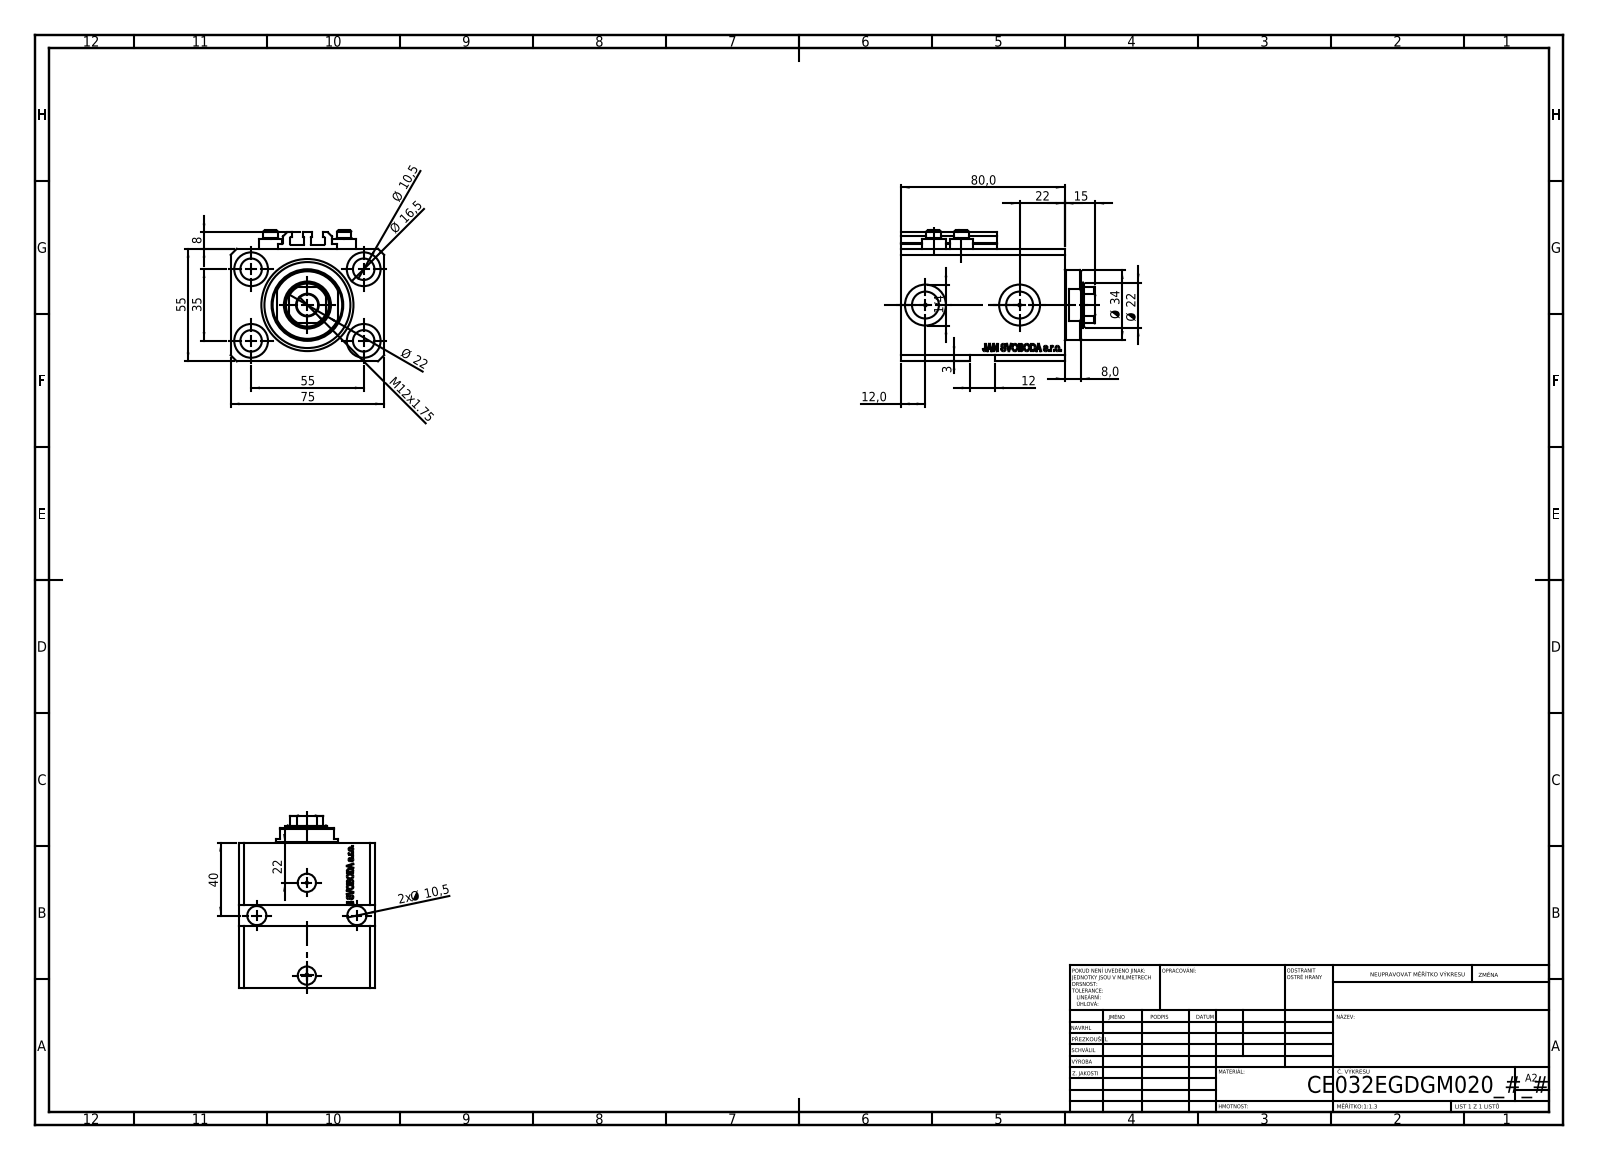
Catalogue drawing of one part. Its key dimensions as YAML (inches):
part_name: "ALLEN BOLT V250CE; V250CE_C_VCP; V250CE_VC_E; V250CE_E_Body"
step_written_by: "SolidWorks 2019 (CONFIG_CONTROL_DESIGN)"
units: inches
bodies: {solids: 8, faces: 1080, planar: 518, cylindrical: 138, other: 424}
overall_size: [3.74, 2.953, 2.52]
volume: 17.1
surface_area: 117.2
round_holes:
  - {diameter: 0.413, count: 7}
  - {diameter: 0.049, count: 4}
  - {diameter: 0.157, count: 4}
  - {diameter: 0.65, count: 4}
  - {diameter: 0.394, count: 2}
  - {diameter: 0.518, count: 2}
  - {diameter: 0.787, count: 2}
  - {diameter: 0.866, count: 1}
  - {diameter: 1.26, count: 1}
  - {diameter: 1.772, count: 1}
round_bosses_or_shafts:
  - {diameter: 0.457, count: 4}
  - {diameter: 0.276, count: 4}
  - {diameter: 1.339, count: 1}
partial_cylinders:
  - {radius: 0.008, count: 10}
  - {radius: 0.413, count: 1}
face_to_face_distances: [2.165, 2.953, 0.591, 3.15, 2.559, 0.118, 0.39, 2.169, 2.76, 2.126]
hole_center_spacings: [1.283, 2.165, 0.535, 0.555, 0.783, 0.792, 1.016, 1.121]
